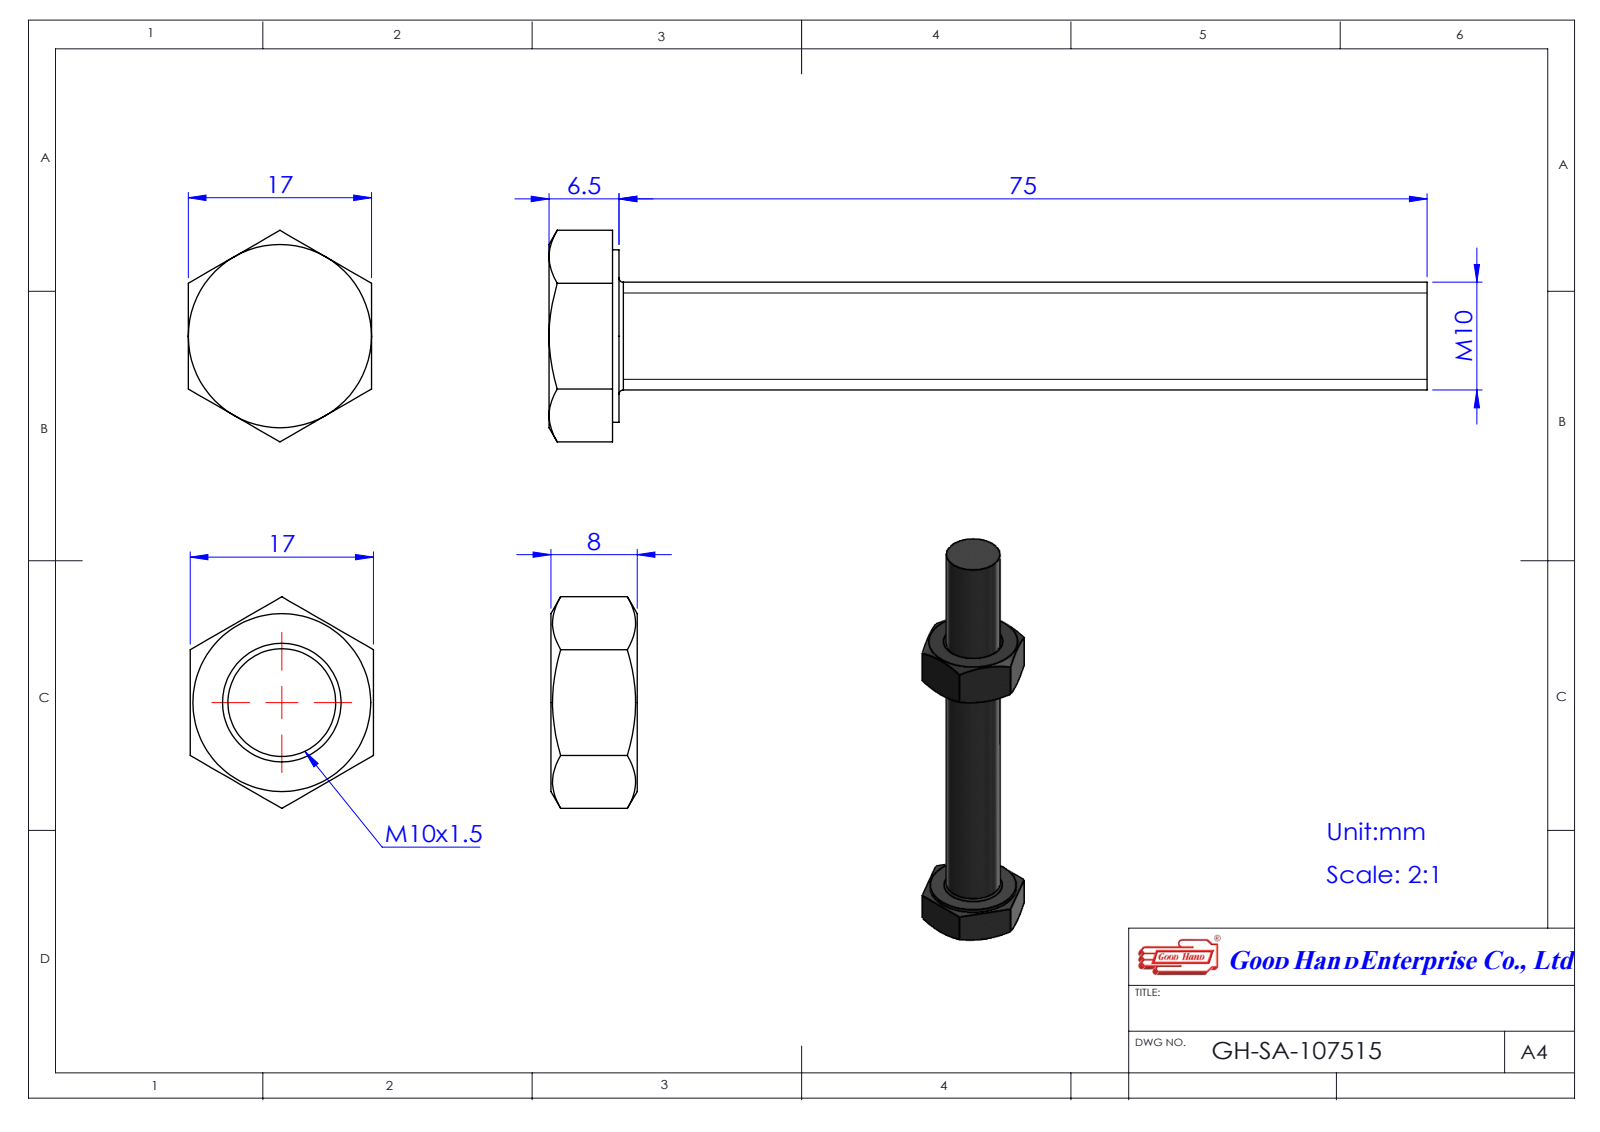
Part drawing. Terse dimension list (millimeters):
name: 7210075K(廠內實物)_JIS B 1180 Continuous thread hexagon head bolt A M10 x 70 --N; 6200100K(DIN934_JIS_); SA-107515
written by: SolidWorks 2016 (AUTOMOTIVE_DESIGN)
unit: mm
bodies: 2 solids, 40 faces (18 planar, 6 cylindrical, 16 other)
size: 81.5 × 19.63 × 17
volume: 8 830 mm³; area: 4 229 mm²
holes: 1× ⌀10
bosses: 1× ⌀16
face distances: 17, 61.75, 53.75, 8, 6.5, 47.25, 55.25, 81.5, 75, 27.75
